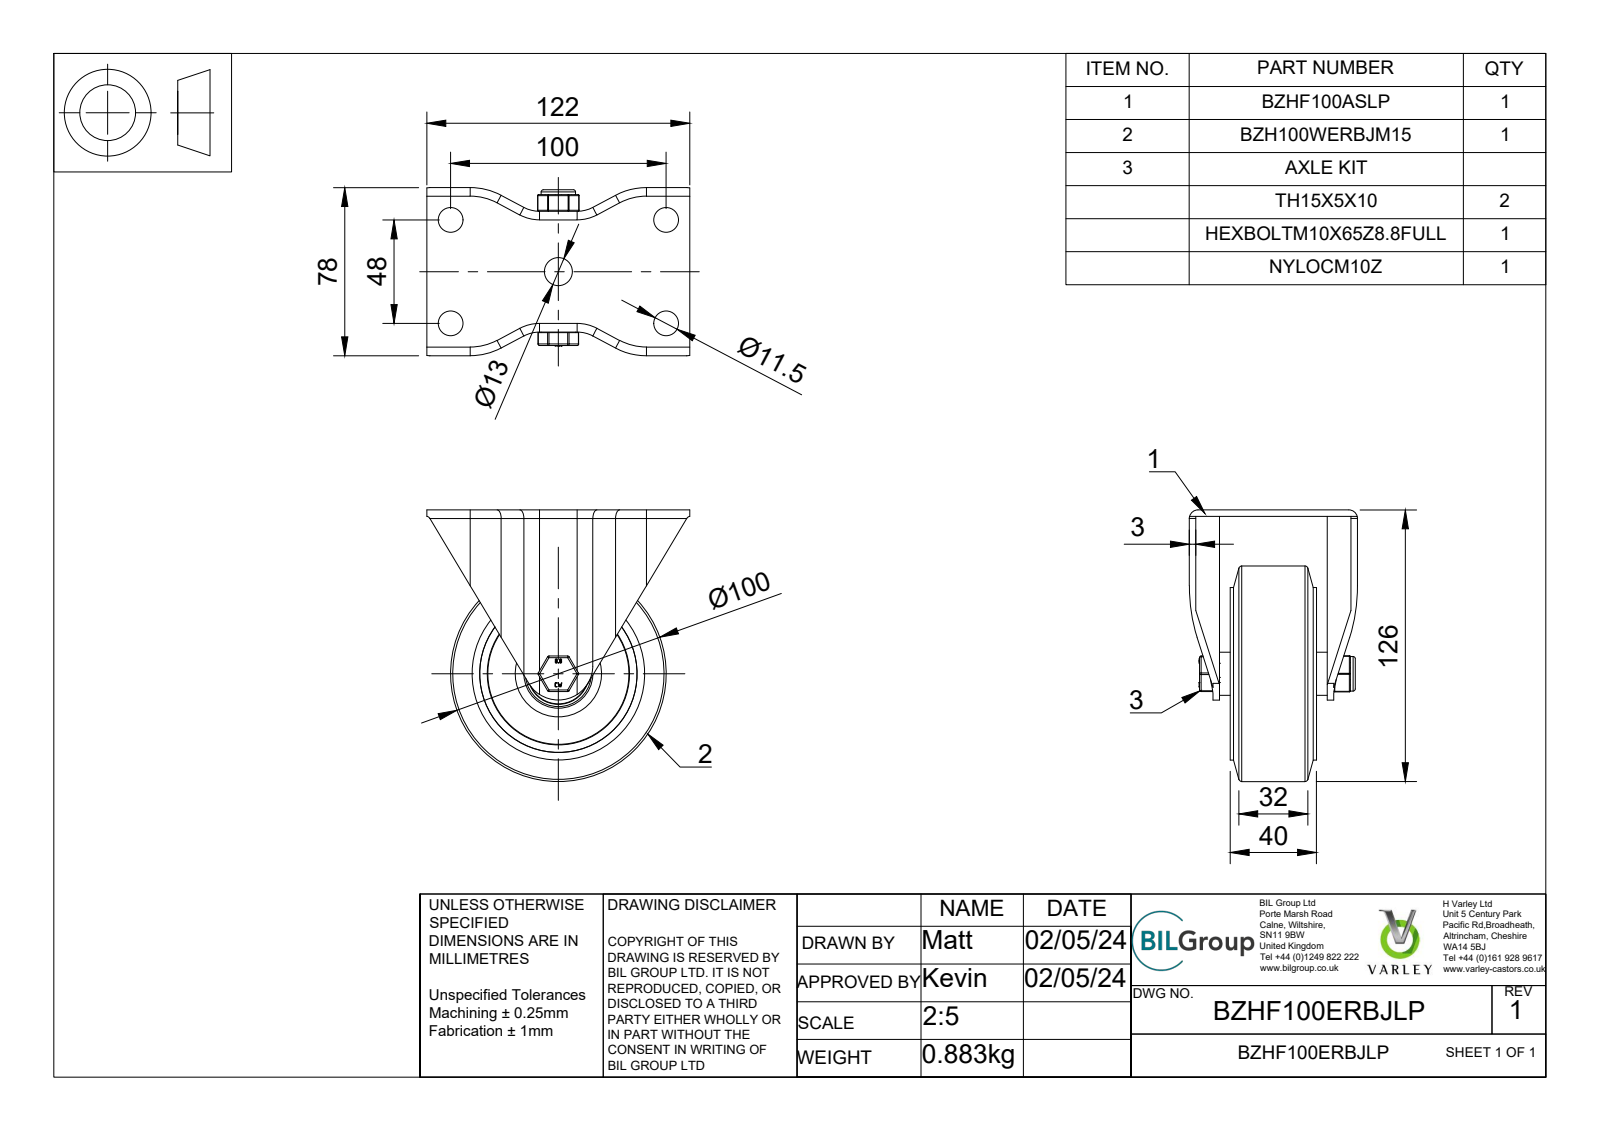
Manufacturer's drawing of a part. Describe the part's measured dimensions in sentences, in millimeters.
The part is named "BZHF100ERBJLP v3; BZHF100ASLP - 50 v1; ZINC PLATED PRESSED STEEL BRACKET; BZH100WERBJM15 v1 (+8 more)". Its 3-D file was written by "Autodesk Translation Framework v12.20.1.177 (AUTOMOTIVE_DESIGN)". It is 37 solids with 1075 faces: 427 planar, 241 cylindrical and 407 other. Overall it measures 126 by 122 by 78 millimeters. Its volume is 288 656 cubic millimeters and its surface area 125 077 square millimeters. Round holes: 4 of diameter 11.5, 1 of diameter 10, 1 of diameter 10.5, 1 of diameter 10.8, 1 of diameter 12, 1 of diameter 13, 1 of diameter 15, 1 of diameter 18, 1 of diameter 20, 1 of diameter 21, 1 of diameter 27.4, 1 of diameter 32. Round bosses or shafts: 1 of diameter 100, 1 of diameter 80, 1 of diameter 40, 1 of diameter 28.4, 1 of diameter 28, 1 of diameter 21.6, 1 of diameter 16, 1 of diameter 14.75. Partial cylindrical surfaces (rounded edges, fillets, slot ends): 18 of radius 0.5, 12 of radius 0.75, 8 of radius 4, 4 of radius 15.5, 4 of radius 30.5, 2 of radius 2, 1 of radius 11.47, 1 of radius 13.47. The main face-to-face distances are 3, 8, 24, 16, 32, 40, 5, 45, 21, 29. The hole center spacings are 55.46, 48, 100, 110.92.
